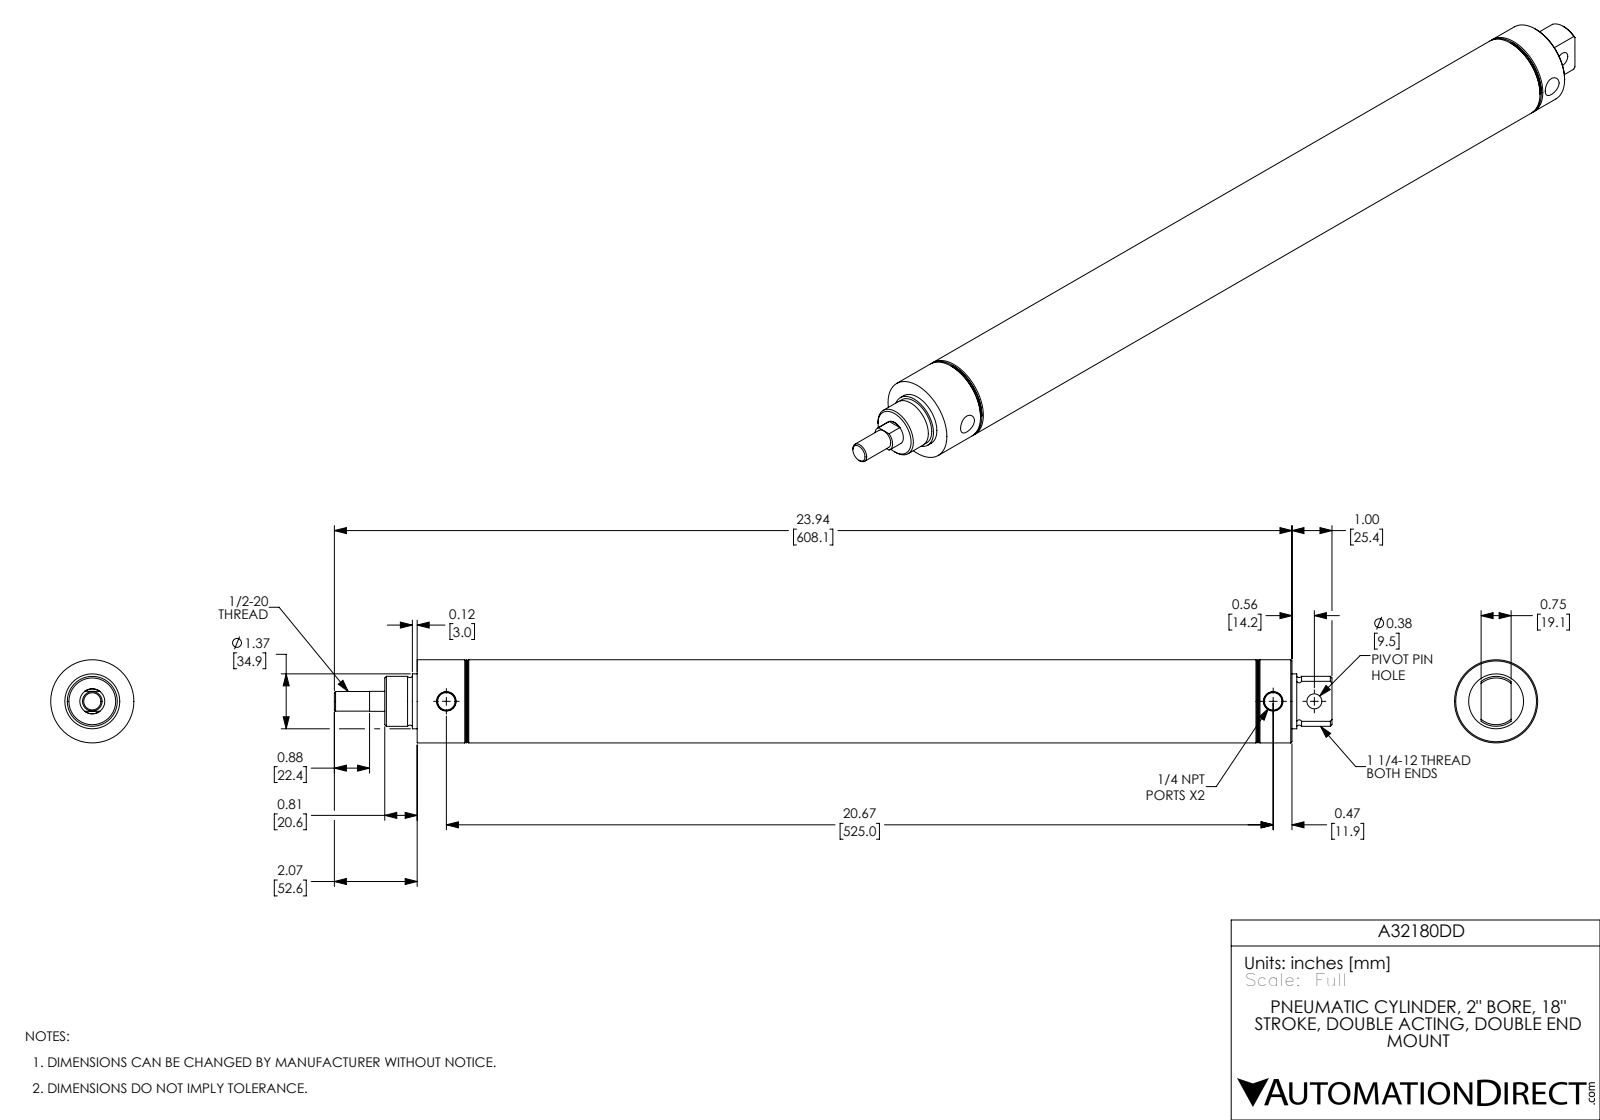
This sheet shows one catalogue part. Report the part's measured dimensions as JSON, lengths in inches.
{"part_name": "A32180DD-MainBody; A32180DD-Rod; A32180DD", "step_written_by": "SolidWorks 2017 (AUTOMOTIVE_DESIGN)", "units": "inches", "bodies": {"solids": 2, "faces": 88, "planar": 20, "cylindrical": 30, "other": 38}, "overall_size": [24.94, 2.08, 2.08], "volume_in3": 25.12, "surface_area_in2": 338.3, "round_holes": [[0.438, 2], [0.375, 1], [0.625, 1], [2, 1]], "round_bosses_or_shafts": [[2.08, 1], [1.373, 1], [1.25, 1], [0.491, 1]], "face_to_face_distances": [1.685, 20.185, 0.5, 18.5, 0.5, 18.5, 18, 20.185, 19.685, 1.685], "hole_center_spacings": [1.03, 20.67, 21.7]}
